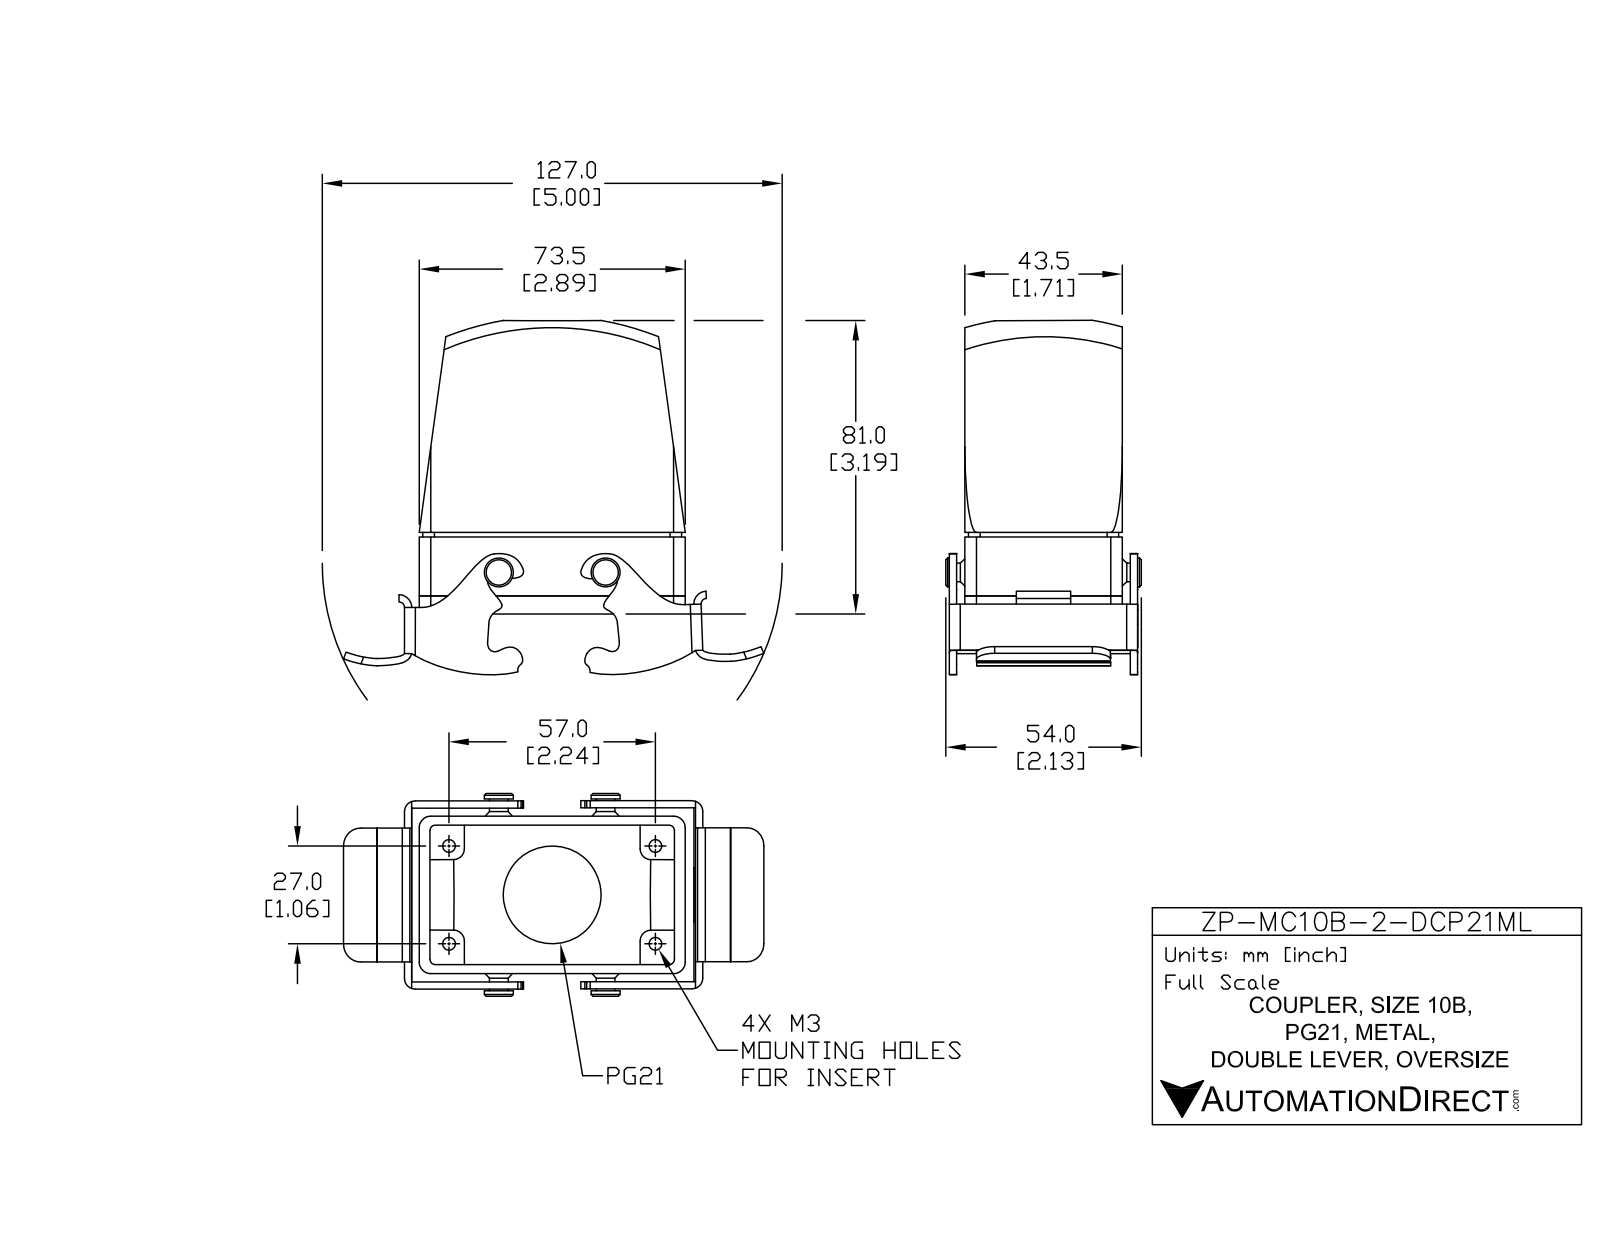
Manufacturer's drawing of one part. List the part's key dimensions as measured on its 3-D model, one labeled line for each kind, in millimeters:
Part name (STEP PRODUCT): ZP-MC10B-2-DCP21ML
STEP written by: SolidWorks 2011 (AUTOMOTIVE_DESIGN)
Units: millimetres
Bodies: 10 solids, 294 faces (138 planar, 142 cylindrical, 14 other)
Overall size (bounding box): 132.09 × 94.98 × 56
Volume: 66 350 mm³ · Surface area: 58 838 mm²
Round holes (diameter × count): ⌀3.5 ×4, ⌀27 ×1
Round bosses / shafts (diameter × count): ⌀8 ×2, ⌀5.17 ×2
Partial cylindrical surfaces — rounded edges, fillets, slot ends (radius × count): R1 ×16, R0.5 ×10, R3.2 ×8, R2 ×6, R3 ×6, R4 ×6, R0.7 ×4, R0.92 ×2
Main face-to-face distances: 2.5, 41, 1, 43.5, 38.5, 45.5, 44.5, 2, 3.5, 42
Hole centre spacings: 32.86, 28.96, 59, 65.72
